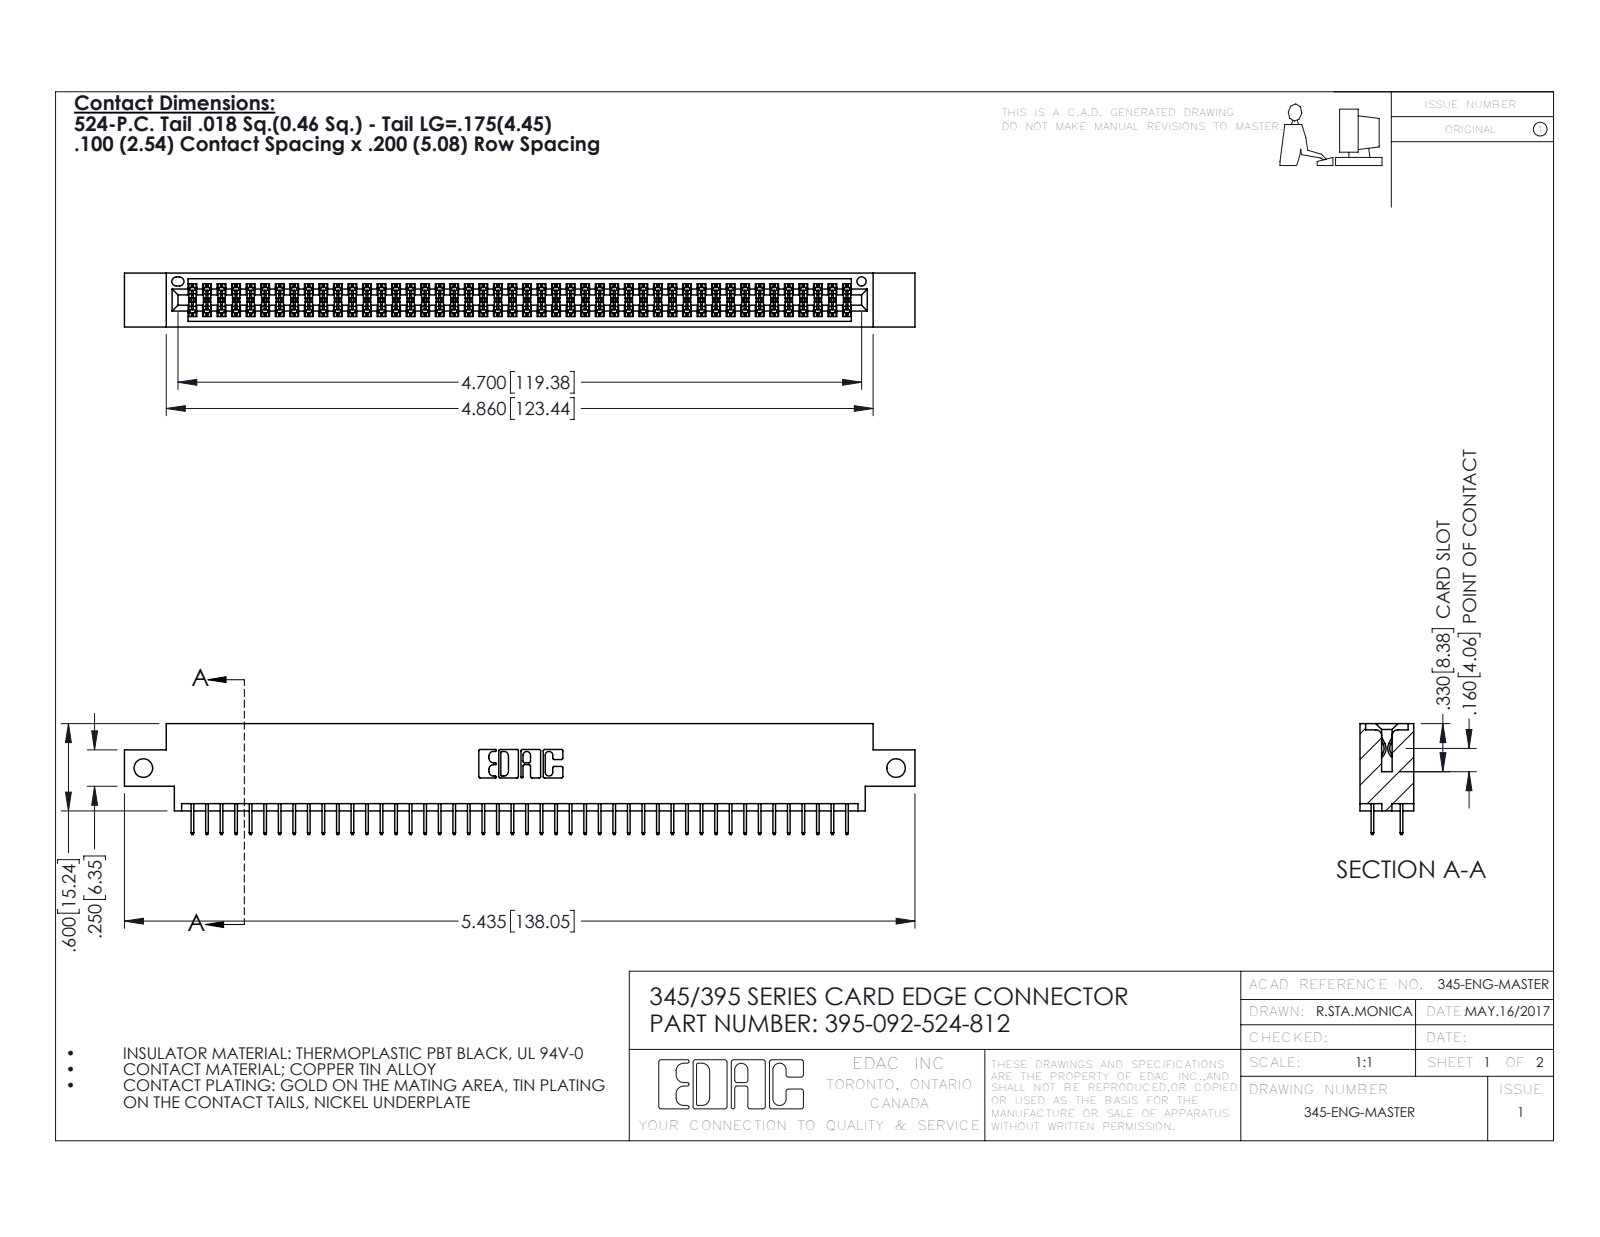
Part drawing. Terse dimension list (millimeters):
name: 395-092-524-812; 345-292-001_345-293-124; 345 Part_0.170 Offset - Side Mount
written by: SolidWorks 2016 (CONFIG_CONTROL_DESIGN)
unit: mm
bodies: 93 solids, 5098 faces (3672 planar, 1426 cylindrical, 0 other)
size: 138 × 19.4 × 9.4
volume: 13 100 mm³; area: 19 090 mm²
holes: 2× ⌀3.3, 1× ⌀1.6
rounds: 138× R0.2, 22× R0.3, 6× R0.2, 6× R0.8, 3× R0.7, 2× R0.4, 2× R0.5, 2× R0.6
face distances: 1.8, 7.6, 9.4, 5.1, 2.5, 6.9, 0.6, 5.7, 4.4, 1.8
hole spacings: 131.4
